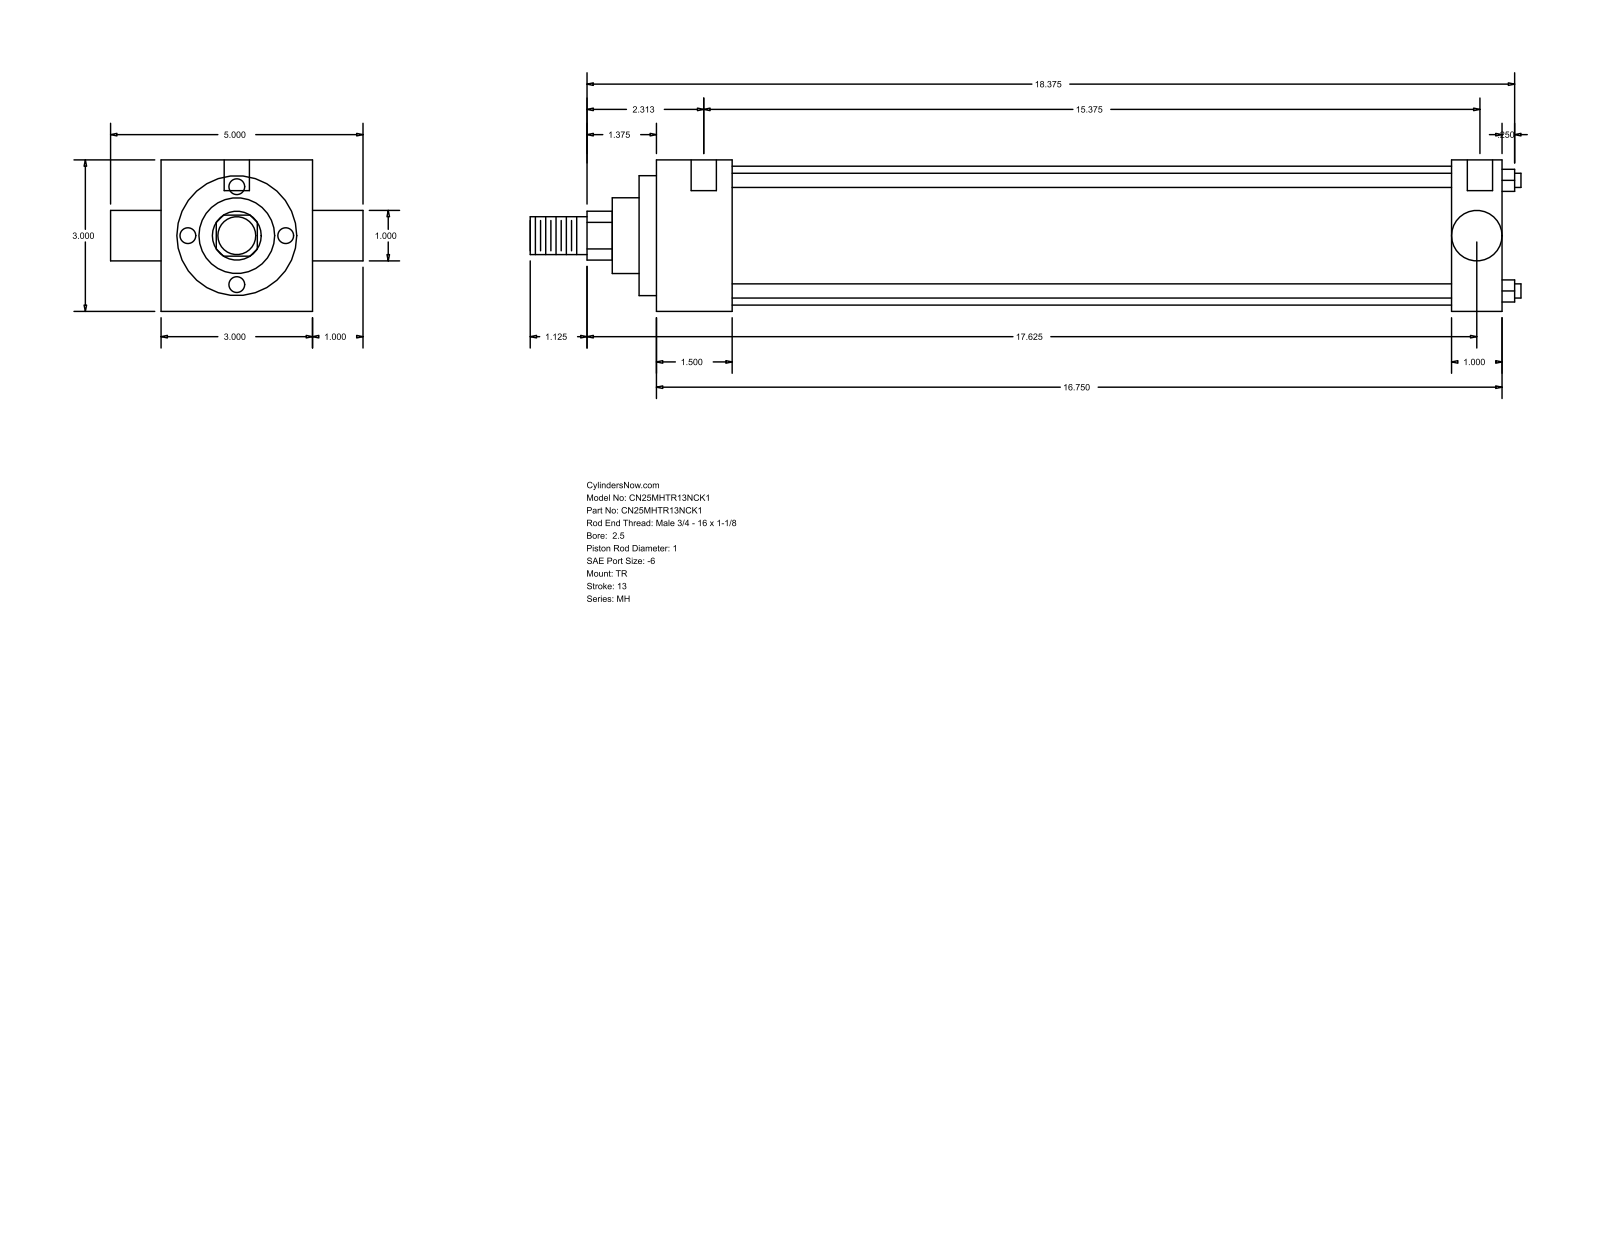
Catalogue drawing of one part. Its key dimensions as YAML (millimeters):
part_name: "MH_TR__0250_1"
step_written_by: "GSSL Pune (CONFIG_CONTROL_DESIGN)"
units: millimeters
bodies: {solids: 0, faces: 86, planar: 61, cylindrical: 25, other: 0}
overall_size: [498.48, 127, 76.2]
round_holes:
  - {diameter: 5.56, count: 3}
  - {diameter: 12.7, count: 2}
round_bosses_or_shafts:
  - {diameter: 7.14, count: 4}
  - {diameter: 69.85, count: 1}
  - {diameter: 60.33, count: 1}
  - {diameter: 38.1, count: 1}
  - {diameter: 25.4, count: 1}
  - {diameter: 25.35, count: 1}
  - {diameter: 19.05, count: 1}
partial_cylinders:
  - {radius: 12.29, count: 1}
face_to_face_distances: [76.2, 425.46, 25.4, 38.11, 387.35, 400.06, 361.95, 8.73, 46.84, 408.79]
hole_center_spacings: [3.18, 4.76, 390.52, 393.7, 395.28, 398.46]
